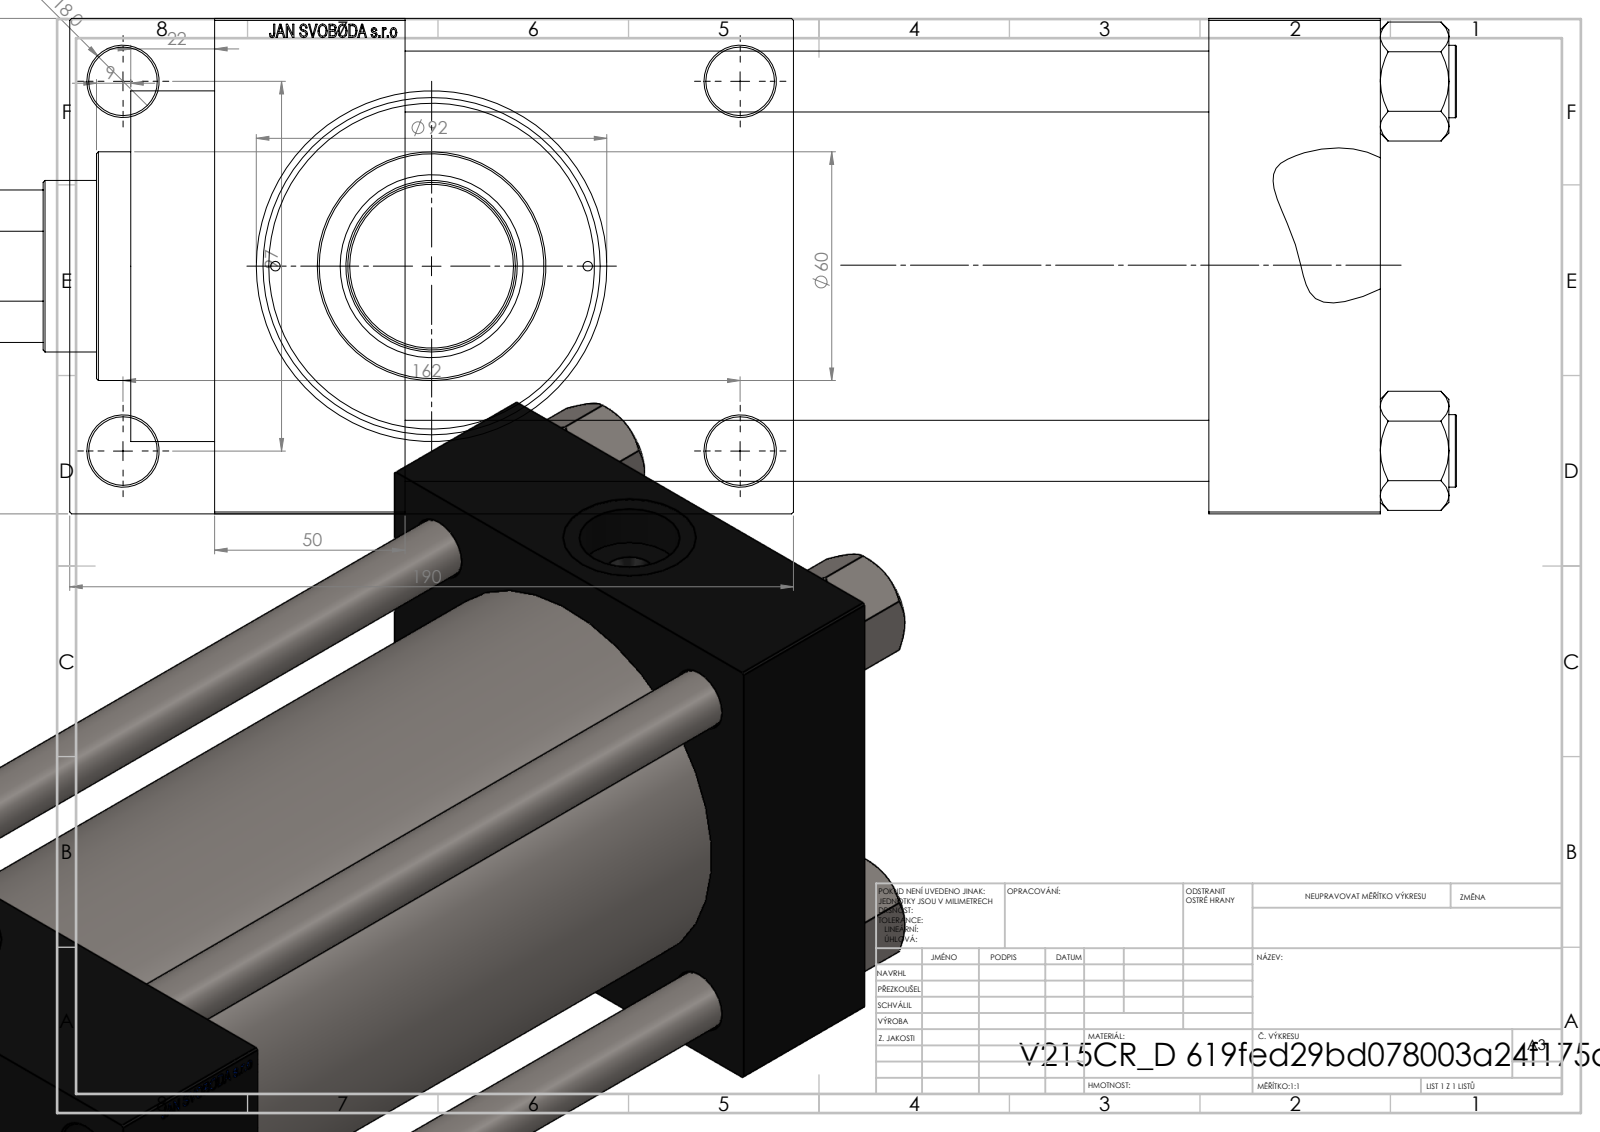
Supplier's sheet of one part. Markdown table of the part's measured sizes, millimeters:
| quantity | value |
| --- | --- |
| part name | NUT_M5_D; V215CR_VCP_D; V215CR_ROD_END_F; V215_VC_A (+2 more) |
| STEP written by | SolidWorks 2019 (CONFIG_CONTROL_DESIGN) |
| units | millimeters |
| bodies | 12 solids, 1173 faces (550 planar, 97 cylindrical, 526 other) |
| overall size | 427 × 190 × 130 |
| volume | 3 130 000 mm³ |
| surface area | 499 162 mm² |
| round holes (diameter × count) | 16 × 4, 18 × 4, 2.5 × 2, 7 × 2, 26.44 × 2, 35 × 2, 31.5 × 1, 45 × 1, 48 × 1, 76 × 1, 85.5 × 1, 100 × 1 |
| round bosses / shafts (diameter × count) | 19 × 4, 106 × 1, 92 × 1, 60 × 1, 44 × 1, 33 × 1 |
| main face-to-face distances | 130, 45, 160, 256, 211, 306, 261, 50, 30, 190 |
| hole center spacings | 32.55, 49.02, 62.87, 68.52, 94.41, 96.9, 101.73, 102.27 |
